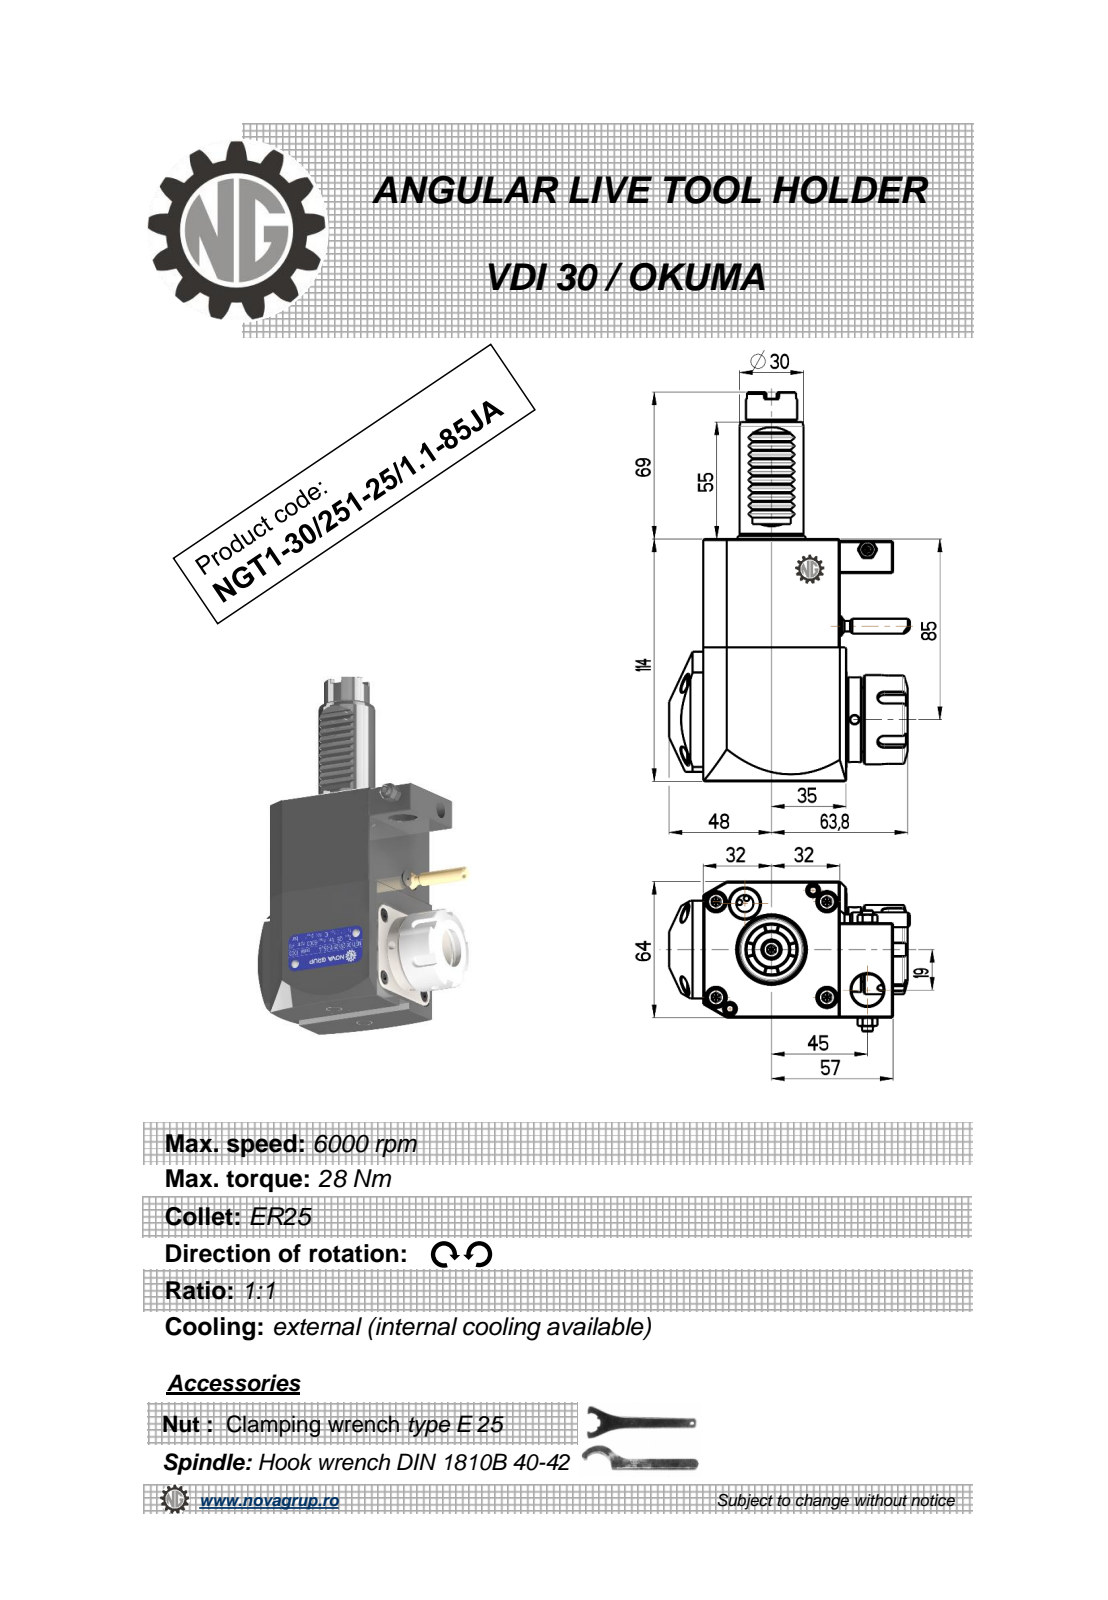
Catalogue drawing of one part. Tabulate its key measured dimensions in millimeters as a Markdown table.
| quantity | value |
| --- | --- |
| part name | NGT1_30_251_25_1_1_85JA |
| STEP written by | PRO/ENGINEER BY PARAMETRIC TECHNOLOGY CORPORATION, 2010280 (CONFIG_CONTROL_DESIGN) |
| units | millimeters |
| bodies | 1 solid, 509 faces (220 planar, 103 cylindrical, 186 other) |
| overall size | 183 × 112.88 × 70.5 |
| volume | 583 902 mm³ |
| surface area | 57 651 mm² |
| round holes (diameter × count) | 4 × 3, 2.5 × 1, 3 × 1, 3.8 × 1, 4.2 × 1, 6 × 1, 9 × 1, 15 × 1, 17 × 1, 20.3 × 1 |
| round bosses / shafts (diameter × count) | 5 × 2, 42 × 1, 40 × 1, 33 × 1, 30 × 1, 24 × 1, 9 × 1, 8.5 × 1 |
| partial cylindrical surfaces (radius × count) | 0.26 × 12, 0.3 × 10, 0.17 × 6, 3 × 5, 3.5 × 4, 160 × 2, 32 × 1 |
| main face-to-face distances | 64, 114, 67.2, 3.2, 67, 3, 16, 1, 113, 15 |
| hole center spacings | 9, 19.94, 32.88, 35.39, 38.95, 46.17, 48.85, 76.5 |
